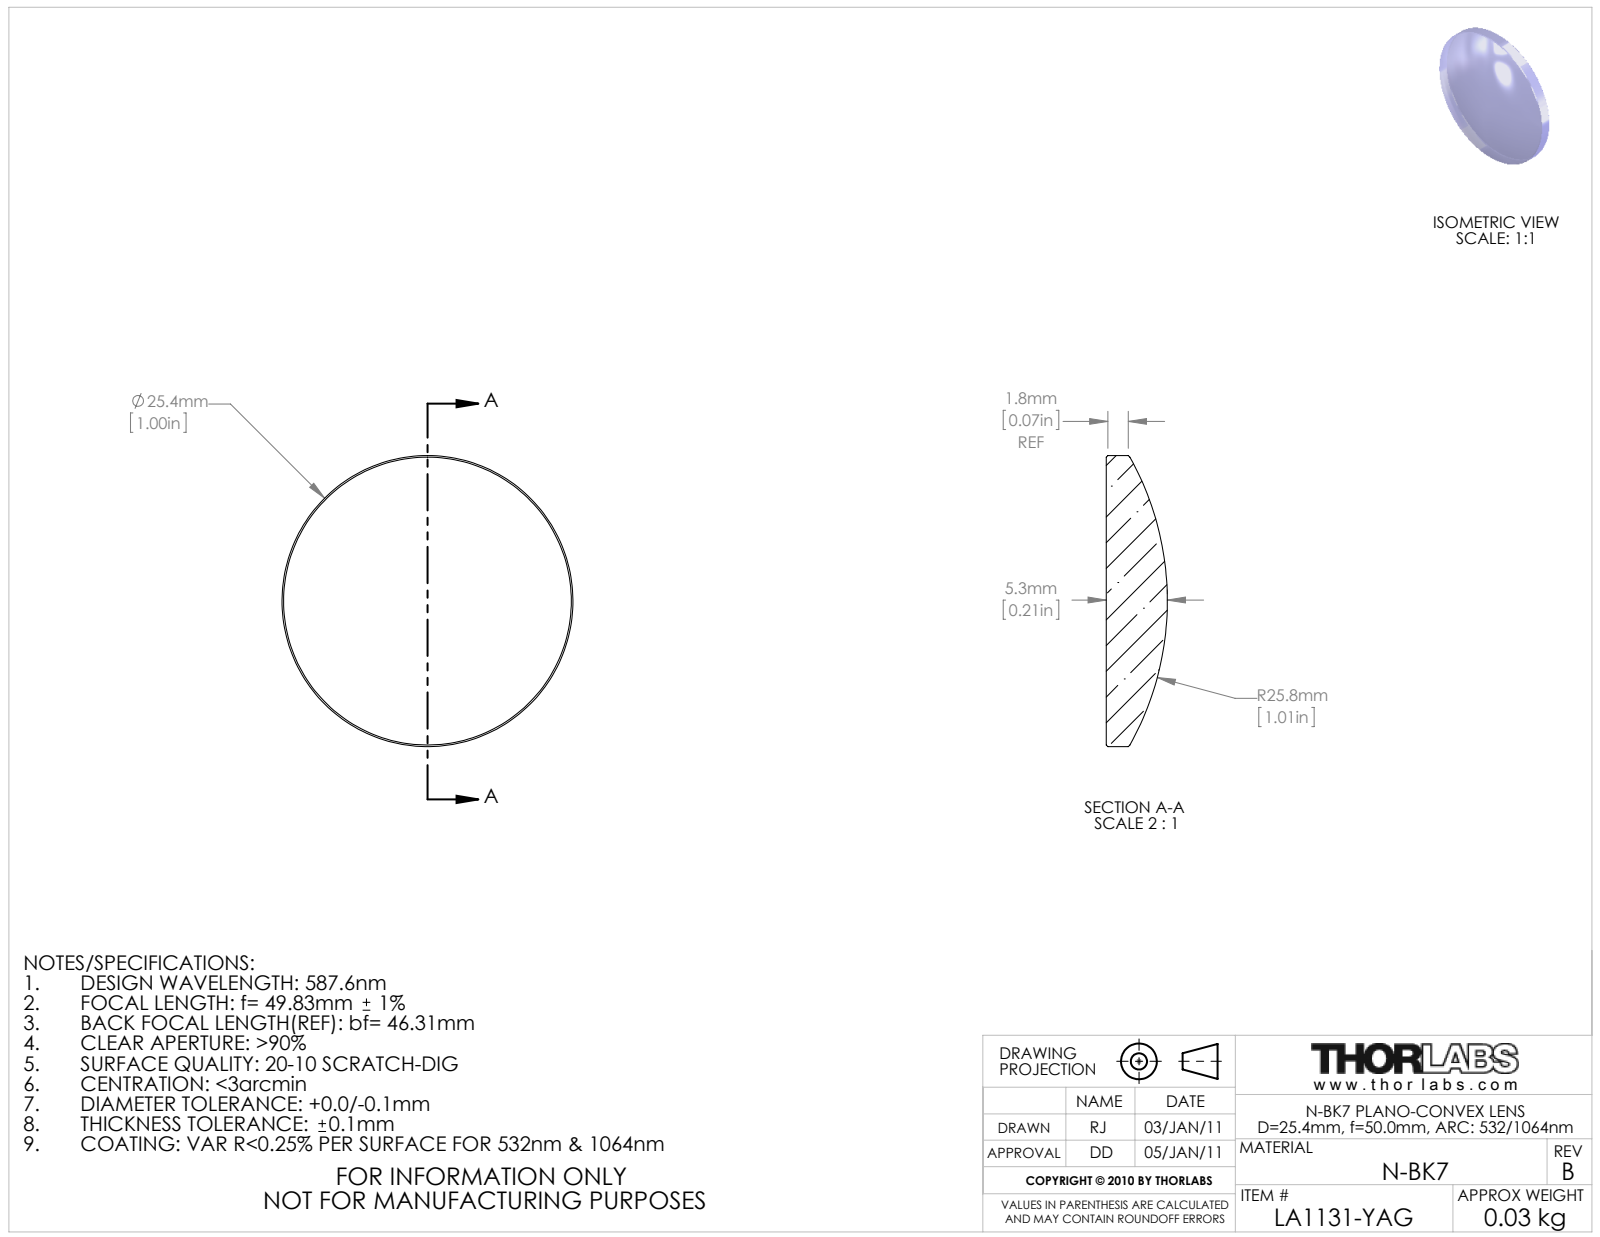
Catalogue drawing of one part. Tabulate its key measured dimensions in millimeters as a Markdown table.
| quantity | value |
| --- | --- |
| part name | 21785-E0W |
| STEP written by | SolidWorks 2011 (AUTOMOTIVE_DESIGN) |
| units | millimeters |
| bodies | 0 solids, 9 faces (1 planar, 2 cylindrical, 6 other) |
| overall size | 25.4 × 25.4 × 5.34 |
| round bosses / shafts (diameter × count) | 25.4 × 1 |
